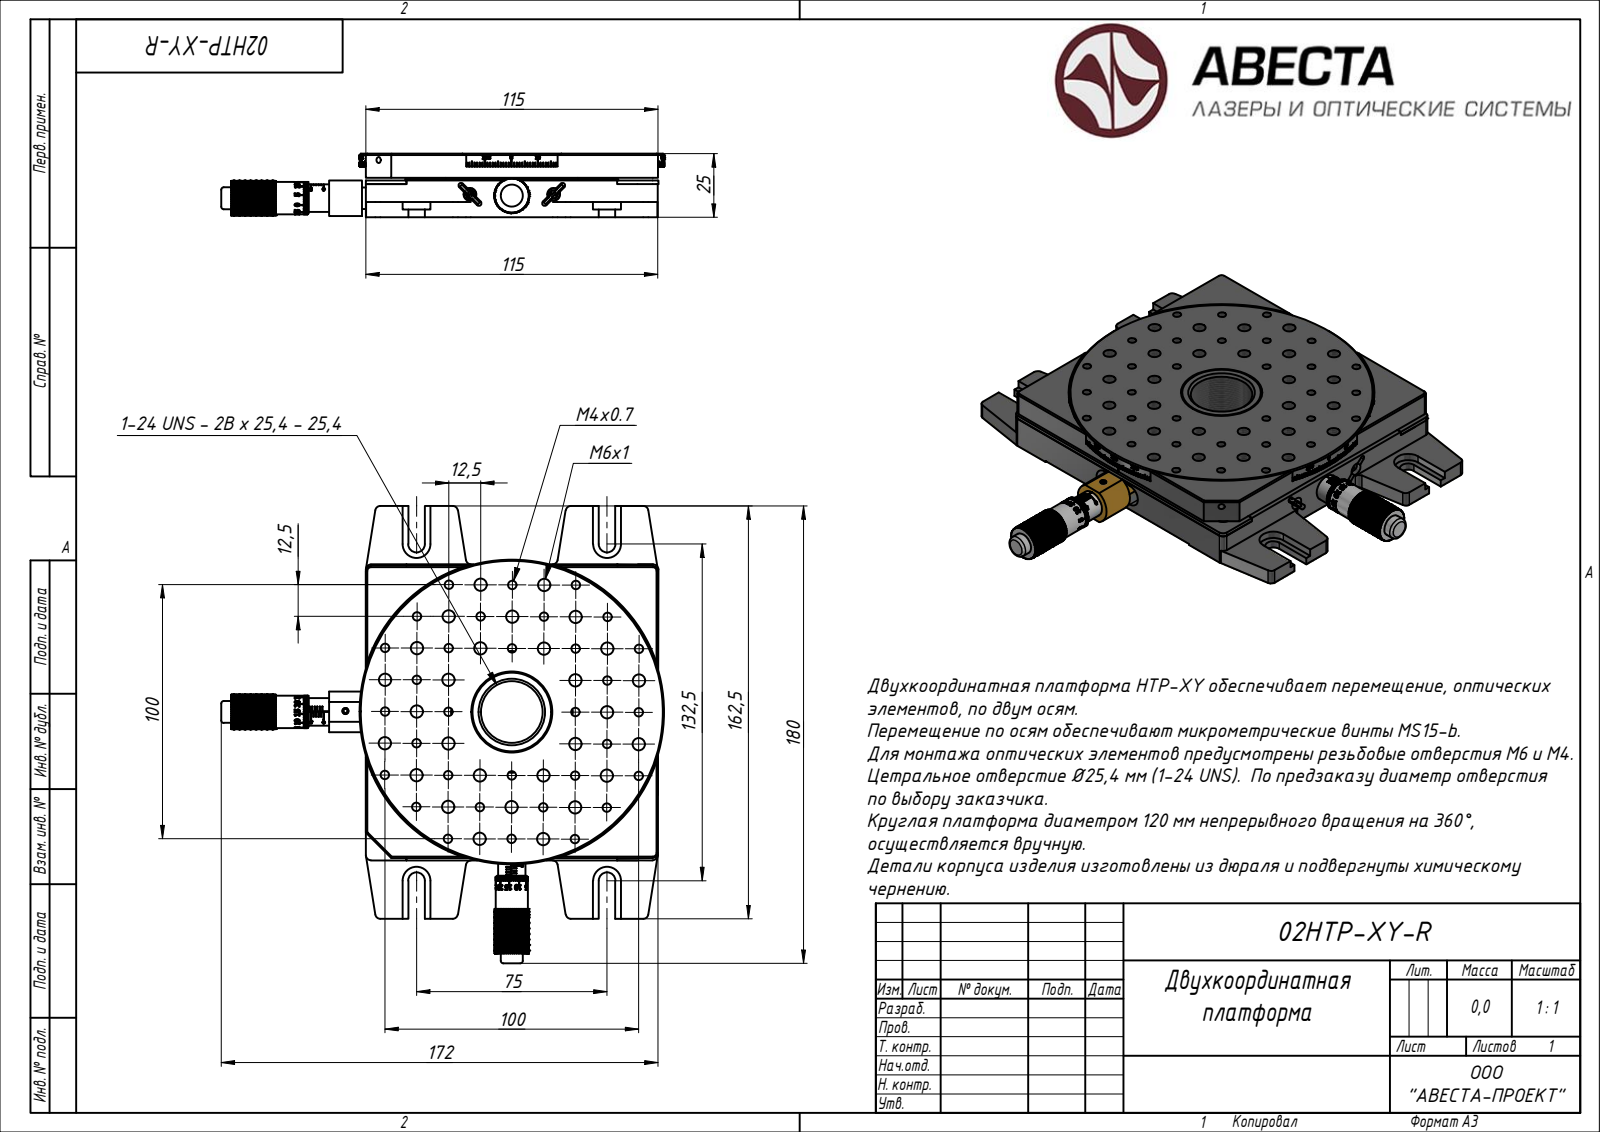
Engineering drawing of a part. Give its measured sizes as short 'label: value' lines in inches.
name: 02HTP-XY(R)_Shrinkwrap_1
written by: Autodesk Inventor 2020 (AUTOMOTIVE_DESIGN)
unit: in
bodies: 8 solids, 10230 faces (7313 planar, 1123 cylindrical, 1794 other)
size: 7.089 × 6.87 × 0.984
volume: 15.18 in³; area: 175.7 in²
holes: 32× ⌀0.128, 28× ⌀0.194, 14× ⌀0.097, 12× ⌀0.062, 7× ⌀0.079, 7× ⌀0.157, 5× ⌀0.197, 4× ⌀0.138, 2× ⌀0.122, 2× ⌀0.217, 2× ⌀0.374, 2× ⌀0.433
bosses: 6× ⌀0.028, 4× ⌀0.118, 2× ⌀0.531, 2× ⌀0.5, 2× ⌀0.425, 2× ⌀0.341, 2× ⌀0.126, 2× ⌀0.039
rounds: 63× R0.079, 4× R0.039, 4× R0.128, 4× R0.217, 2× R0.177, 2× R0.212, 2× R0.246, 1× R0.315
face distances: 0.02, 0.374, 0.079, 0.492, 0.551, 0.591, 0.61, 0.413, 0.571, 0.059
hole spacings: 0.696, 0.984, 1.556, 2.509, 3.48, 1.392, 2.201, 1.969
